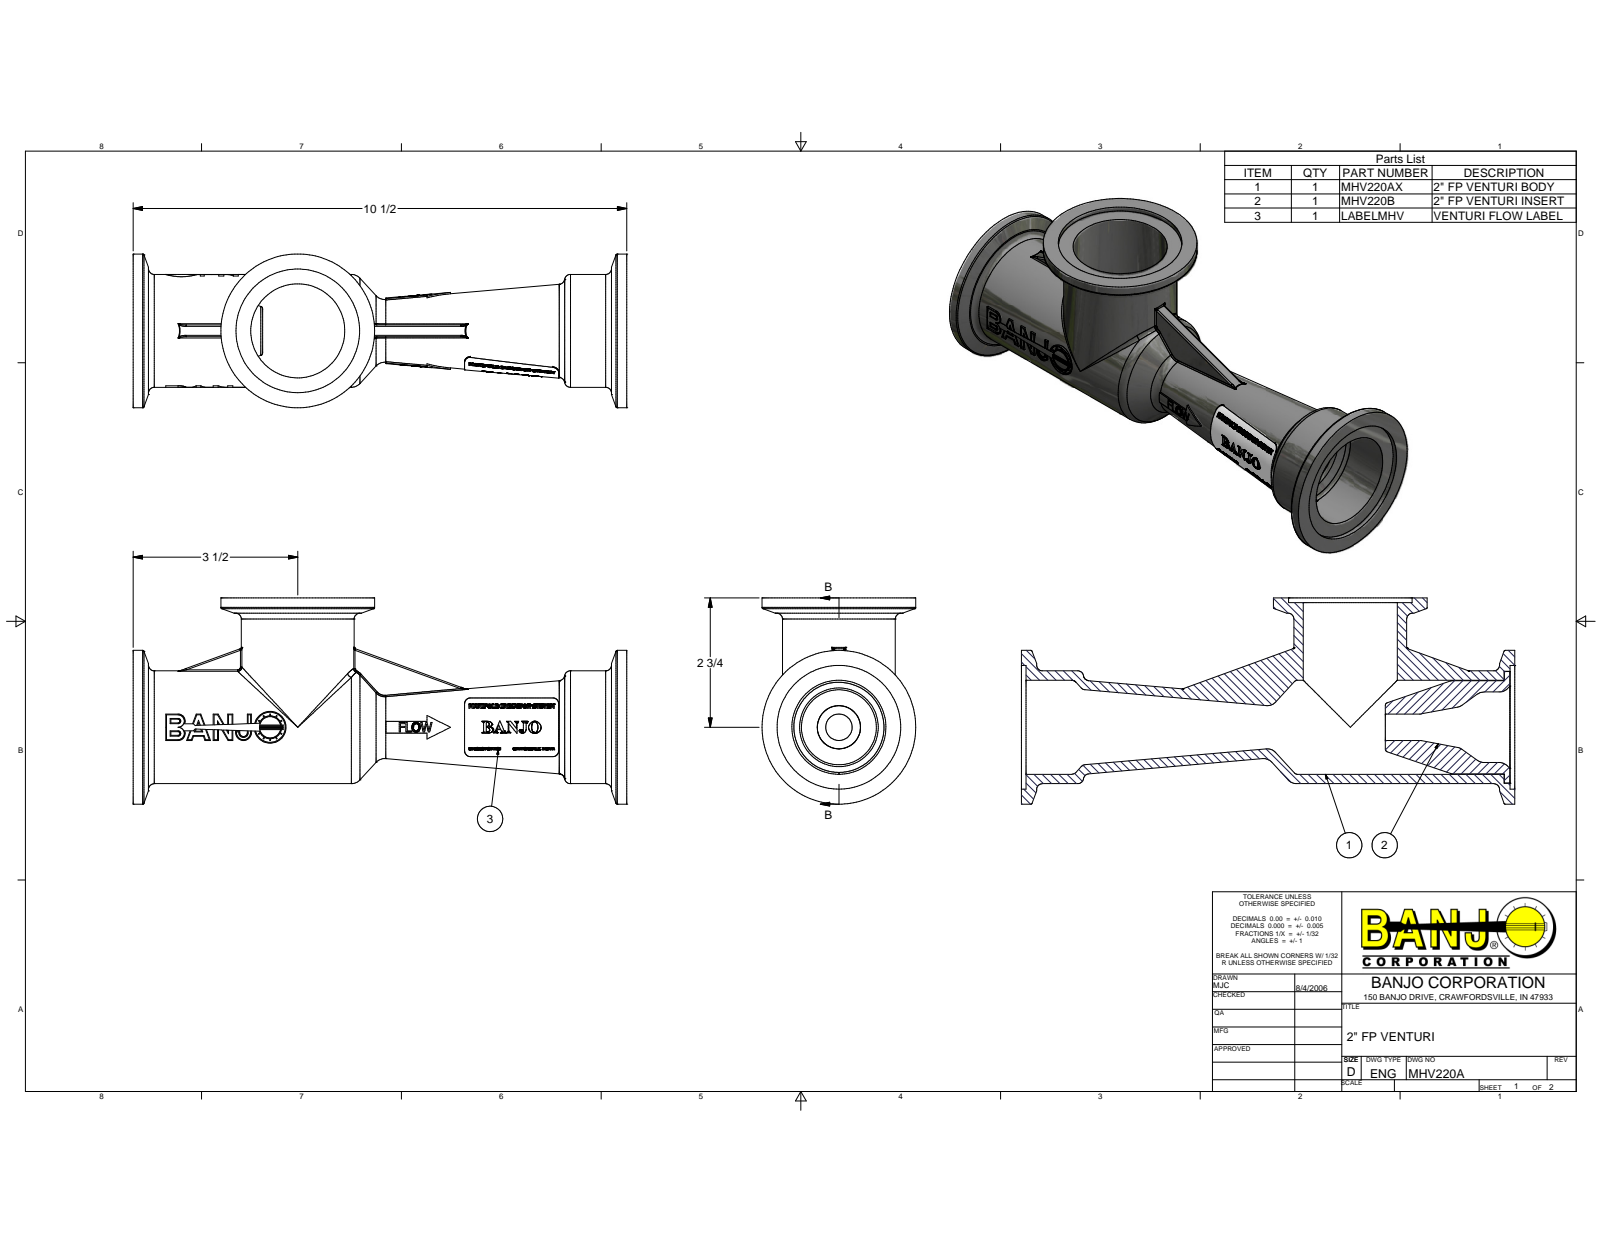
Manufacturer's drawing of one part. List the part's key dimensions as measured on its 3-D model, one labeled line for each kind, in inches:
Part name (STEP PRODUCT): MHV220A; MHV220AX; MHV220B; LABELMHV
STEP written by: Autodesk Inventor 2011 (AUTOMOTIVE_DESIGN)
Units: inches
Bodies: 3 solids, 1668 faces (970 planar, 147 cylindrical, 551 other)
Overall size (bounding box): 10.5 × 4.385 × 3.27
Volume: 22.1 in³ · Surface area: 210.2 in²
Round holes (diameter × count): ⌀0.454 ×2, ⌀0.641 ×2, ⌀2 ×2, ⌀2.63 ×2, ⌀0.563 ×1, ⌀1.5 ×1, ⌀2.38 ×1
Round bosses / shafts (diameter × count): ⌀3.27 ×2, ⌀2.4 ×2, ⌀0.675 ×2, ⌀2.37 ×1, ⌀1.98 ×1
Partial cylindrical surfaces — rounded edges, fillets, slot ends (radius × count): R0.03 ×10, R0.039 ×4, R0.056 ×4, R0.125 ×4, R0.132 ×4, R0.149 ×4, R0.082 ×2, R0.099 ×2
Main face-to-face distances: 0.1, 10.4, 10.5, 0.105, 10.295, 10.395, 0.225, 0.225, 0.12, 10.175
Hole centre spacings: 1.887
